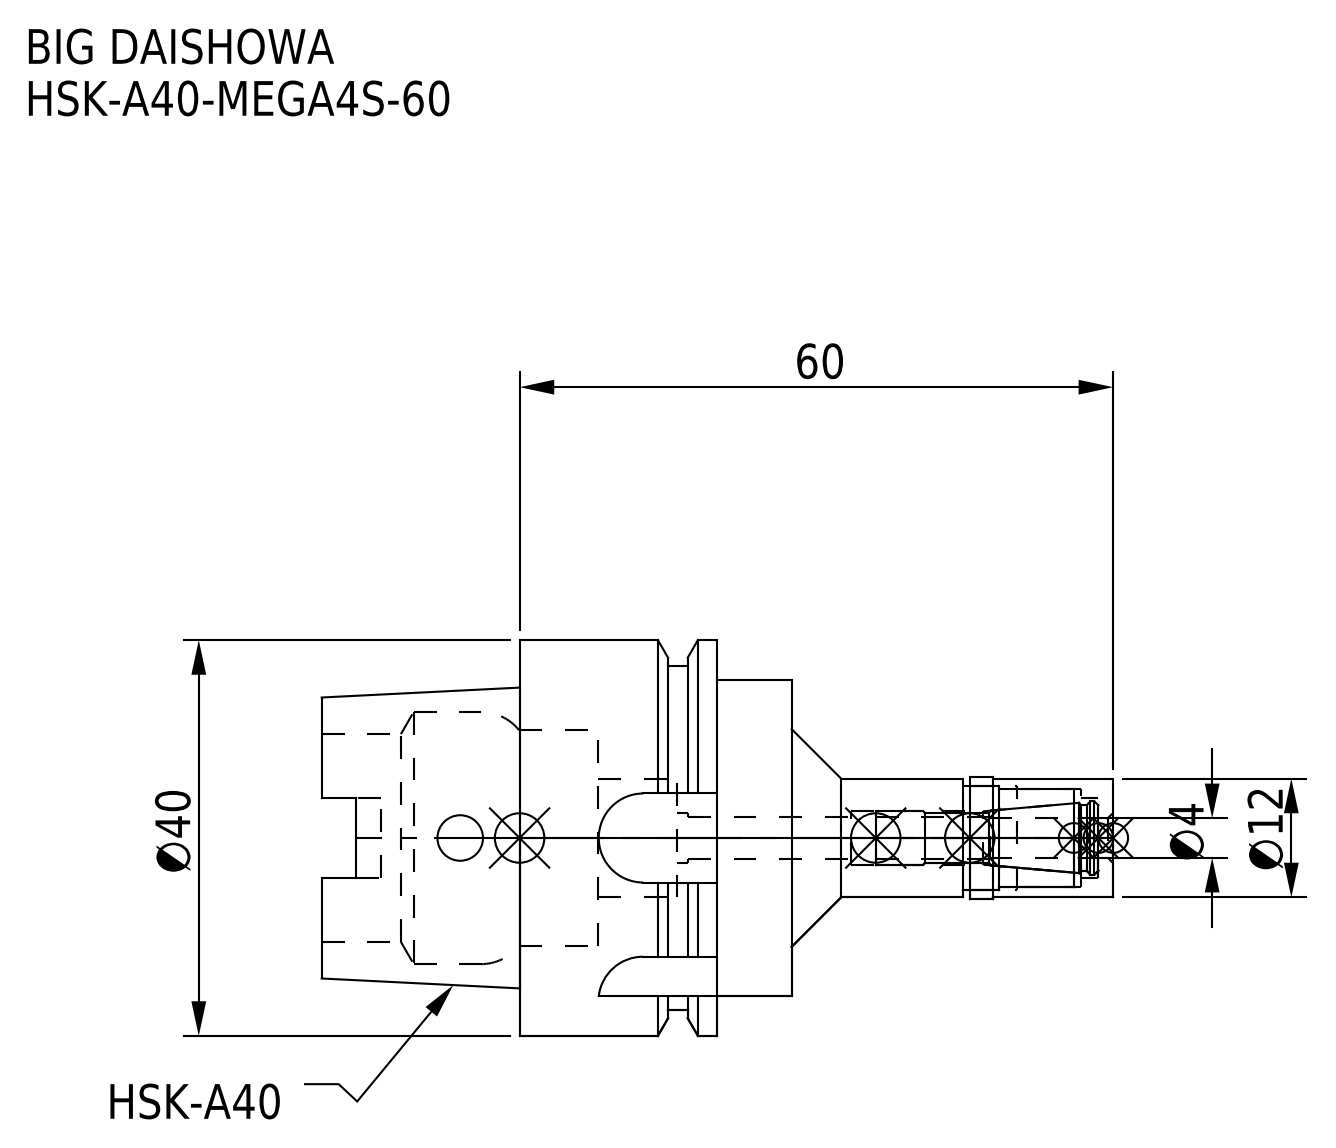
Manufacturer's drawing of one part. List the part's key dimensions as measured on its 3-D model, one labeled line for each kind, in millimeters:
Part name (STEP PRODUCT): HSK-A40-MEGA4S-60_1.stp; DXF_TEMP_ASSY_ASM_4_ASM.stp; HSK-A40-MEGA4S-60; HSK-A40-MEGA4S-60-040.stp (+3 more)
STEP written by: SolidWorks 2019 (CONFIG_CONTROL_DESIGN)
Units: millimetres
Bodies: 2 solids, 123 faces (47 planar, 56 cylindrical, 20 other)
Overall size (bounding box): 80 × 40 × 40
Volume: 33 727 mm³ · Surface area: 12 975 mm²
Round holes (diameter × count): ⌀4.1 ×1, ⌀4.2 ×1, ⌀4.6 ×1, ⌀5 ×1, ⌀5.4 ×1, ⌀8 ×1, ⌀10 ×1, ⌀10.5 ×1, ⌀21 ×1, ⌀21.8 ×1, ⌀25.5 ×1
Round bosses / shafts (diameter × count): ⌀40 ×1, ⌀34.8 ×1, ⌀32 ×1, ⌀12.3 ×1, ⌀12 ×1
Partial cylindrical surfaces — rounded edges, fillets, slot ends (radius × count): R1.88 ×4, R4.5 ×4
Main face-to-face distances: 20, 27.5, 7.5, 7.95, 40, 19.55, 12.05, 47.5, 27.95, 34
